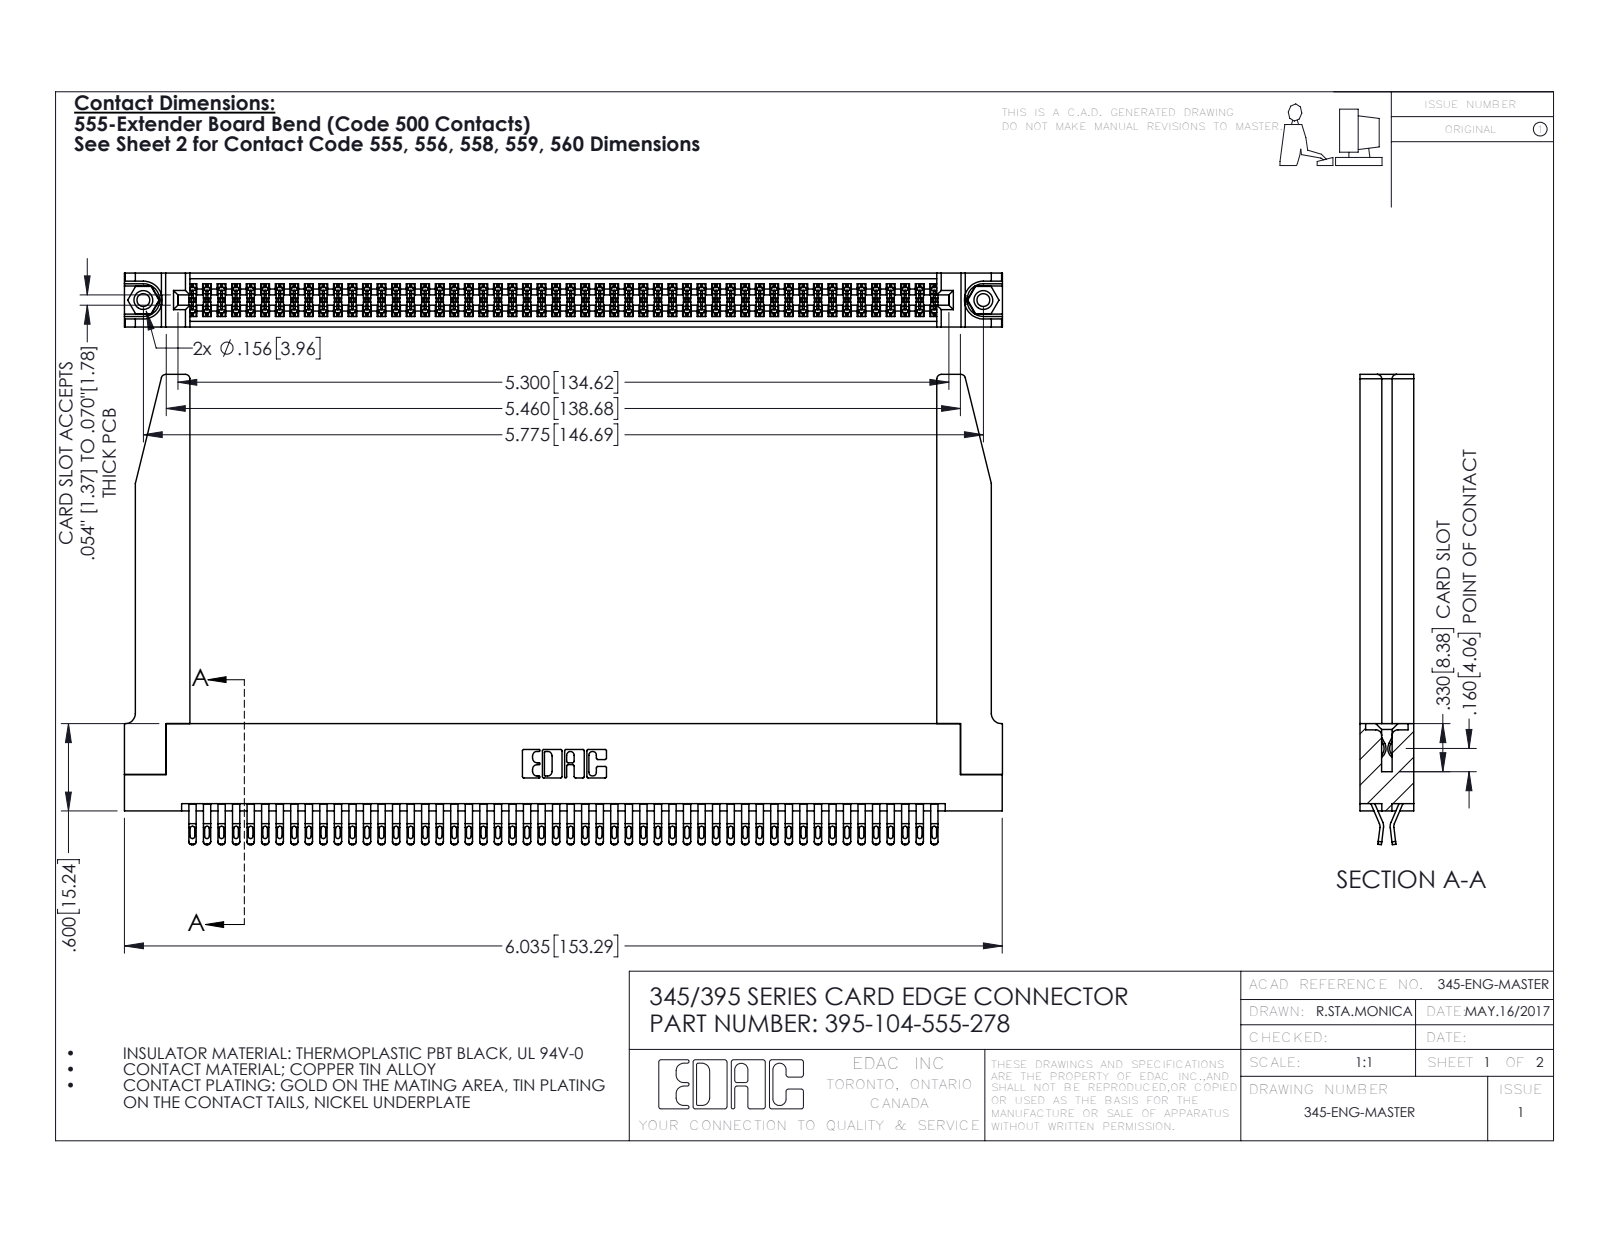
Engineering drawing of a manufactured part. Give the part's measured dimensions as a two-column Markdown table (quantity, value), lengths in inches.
| quantity | value |
| --- | --- |
| part name | 345-250-001_345-250-001-102; 345 Part_Flush Mounting Lugs - 0.156 Dia-TH; 345-292-001_555 Tail; 345-220-078_345-220-078 (+1 more) |
| STEP written by | SolidWorks 2016 (CONFIG_CONTROL_DESIGN) |
| units | inches |
| bodies | 109 solids, 6184 faces (3446 planar, 2686 cylindrical, 52 other) |
| overall size | 6.036 × 3.232 × 0.37 |
| volume | 1.407 in³ |
| surface area | 47.55 in² |
| round holes (diameter × count) | 0.089 × 2, 0.125 × 2, 0.156 × 2, 0.064 × 1 |
| round bosses / shafts (diameter × count) | 0.155 × 2 |
| partial cylindrical surfaces (radius × count) | 0.016 × 260, 0.02 × 208, 0.006 × 156, 0.01 × 22, 0.03 × 8, 0.007 × 6, 0.031 × 6, 0.026 × 3 |
| main face-to-face distances | 0.072, 0.37, 0.298, 0.025, 0.2, 0.098, 0.272, 0.225, 0.175, 0.15 |
| hole center spacings | 0.27, 5.539, 5.775 |
